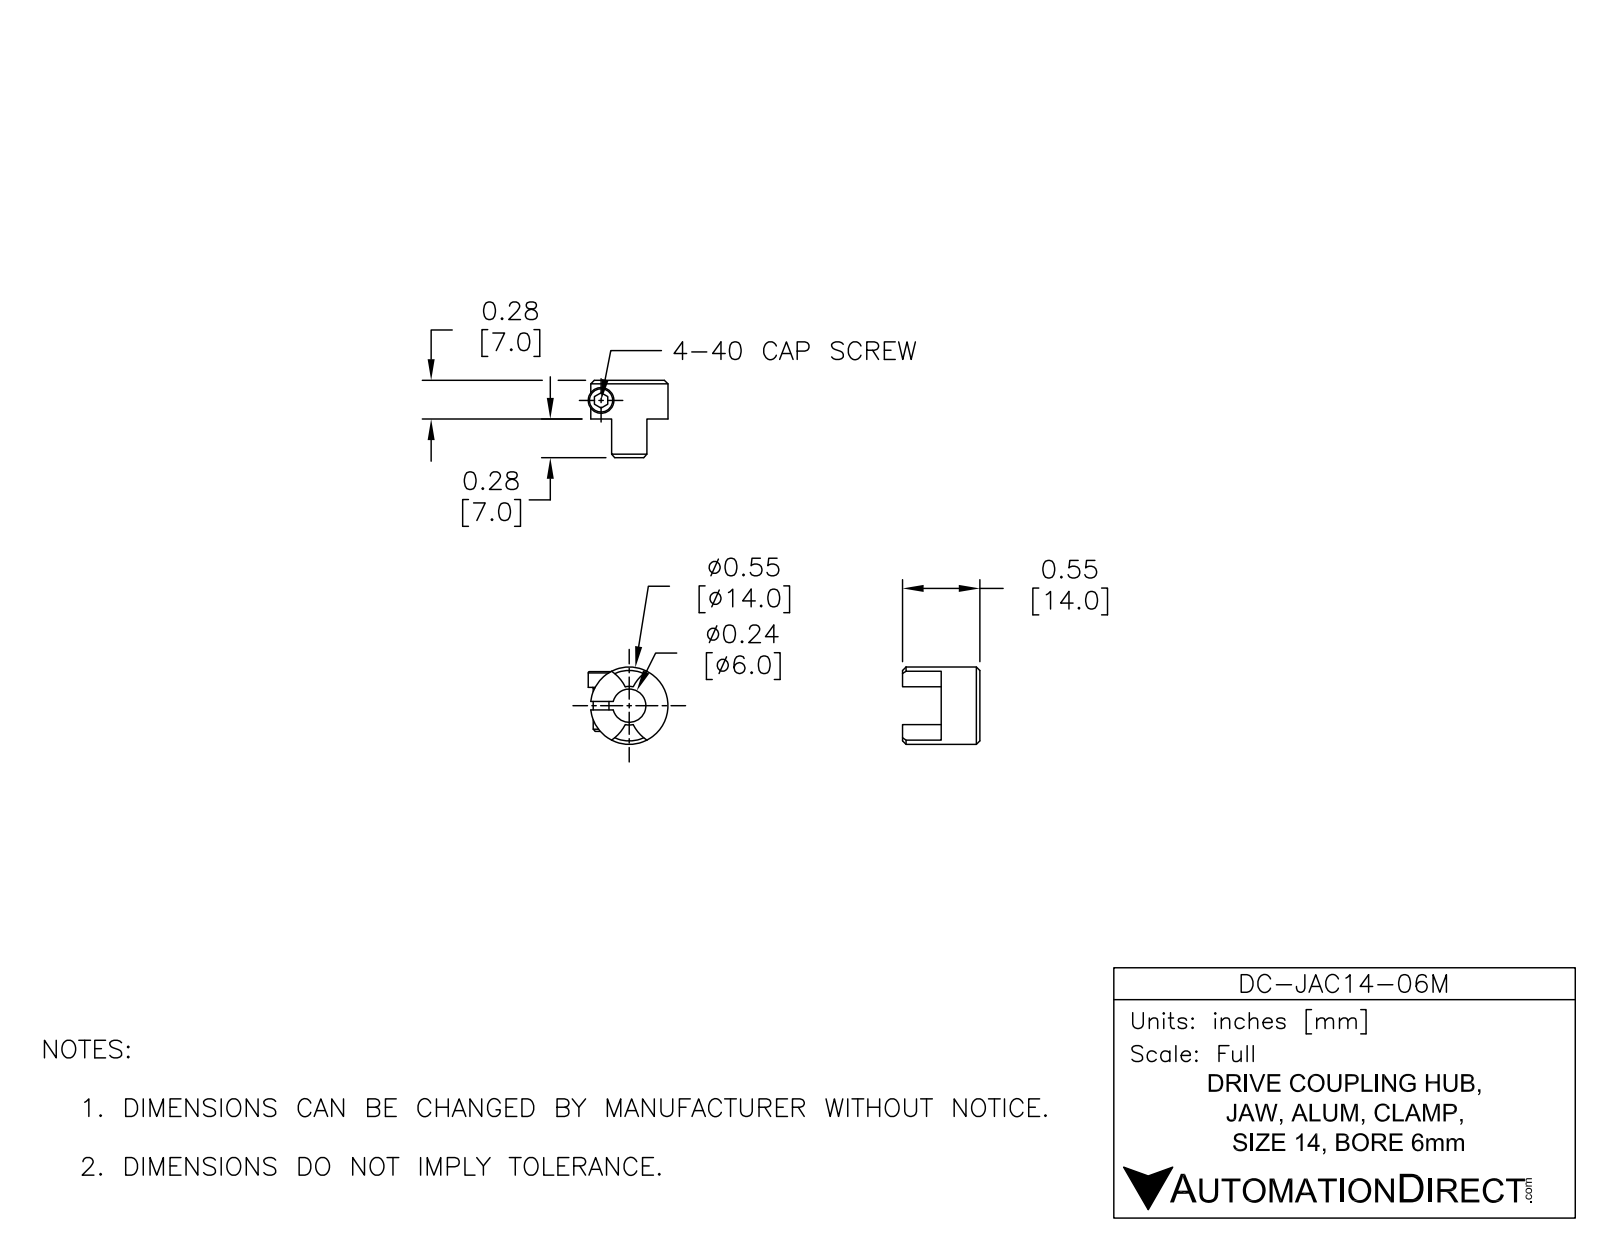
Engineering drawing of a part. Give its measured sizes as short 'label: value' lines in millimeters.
name: DC-JAC14-06M
written by: SolidWorks 2015 (AUTOMOTIVE_DESIGN)
unit: mm
bodies: 1 solid, 30 faces (7 planar, 17 cylindrical, 6 other)
size: 13.97 × 13.97 × 13.93
volume: 923 mm³; area: 943 mm²
holes: 1× ⌀3.28, 1× ⌀6
bosses: 1× ⌀13.97
rounds: 2× R7.52, 1× R2.39, 1× R3.49
face distances: 6.99, 1.52, 13.97, 6.98, 2.54, 4.06
